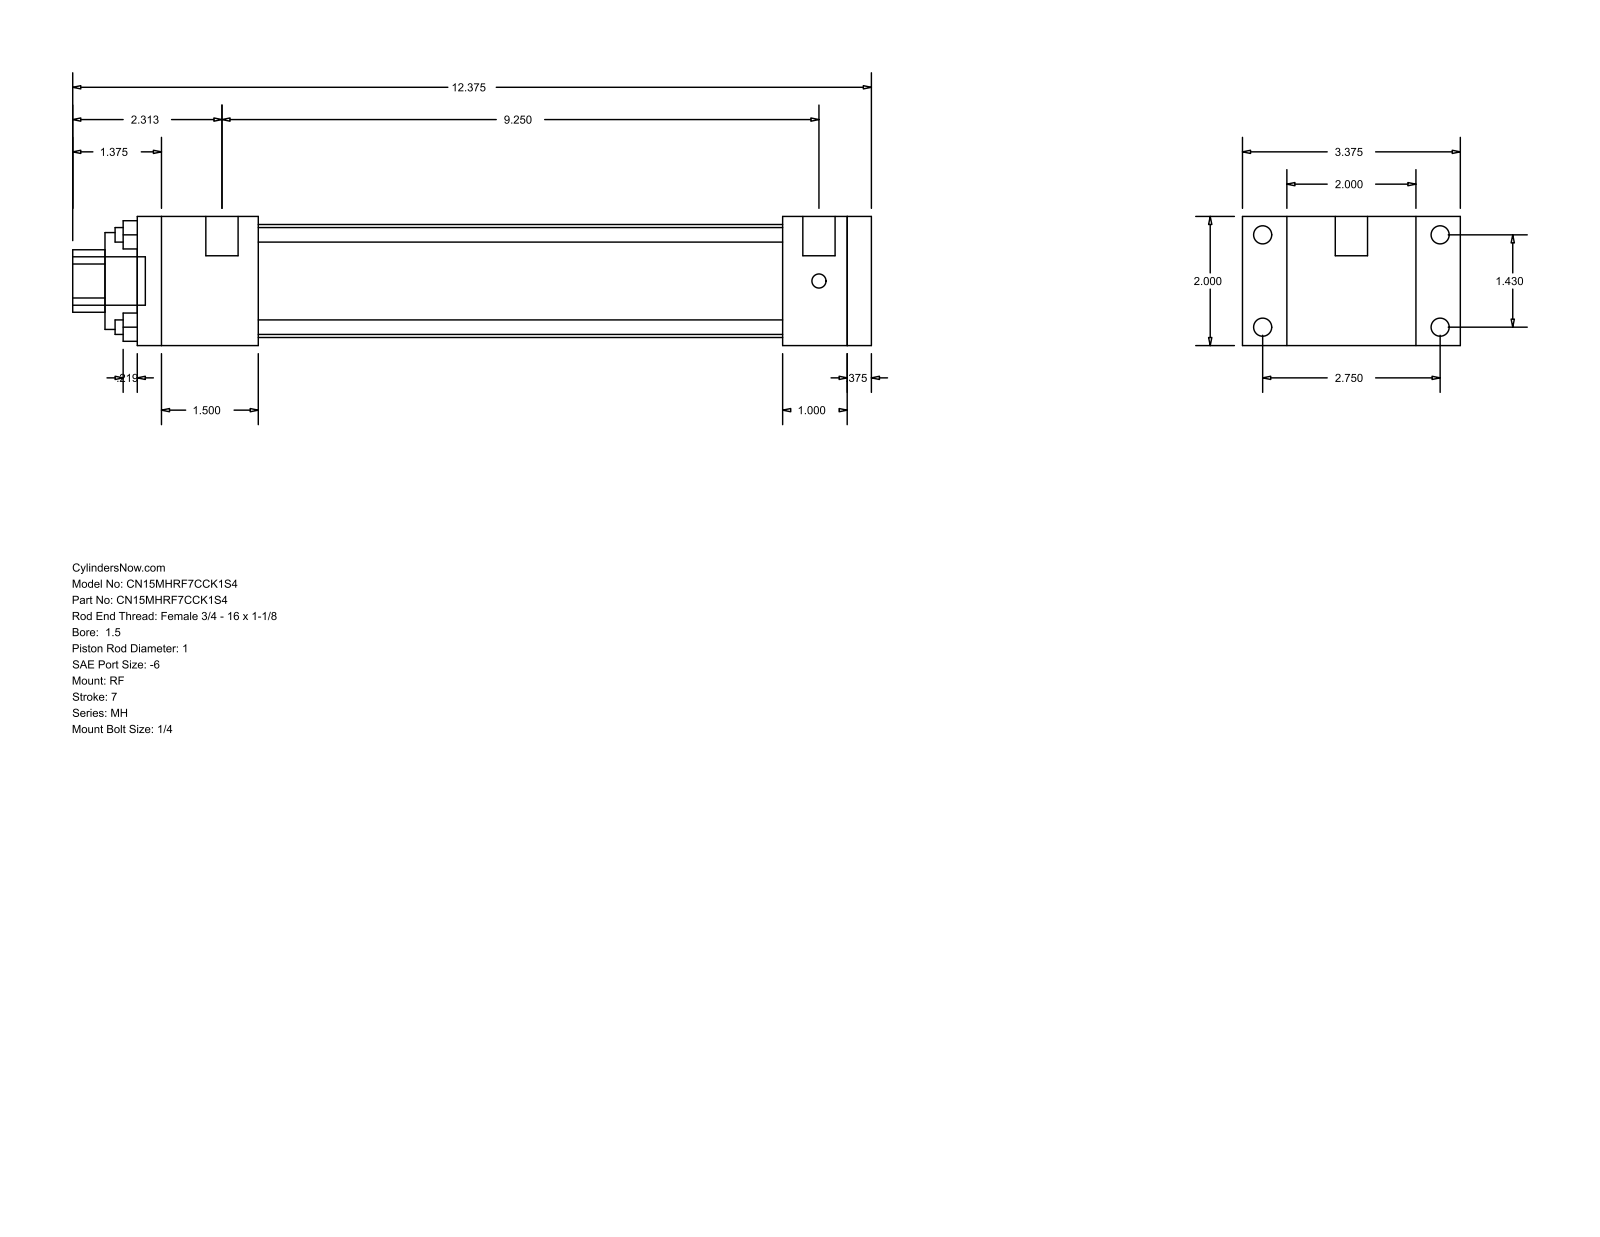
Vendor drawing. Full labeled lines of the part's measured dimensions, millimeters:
Part name (STEP PRODUCT): MH_RF__0150_1
STEP written by: GSSL Pune (CONFIG_CONTROL_DESIGN)
Units: millimetres
Bodies: 0 solids, 92 faces (64 planar, 28 cylindrical, 0 other)
Overall size (bounding box): 314.32 × 85.72 × 50.8
Round holes (diameter × count): ⌀5.71 ×4, ⌀25.4 ×1, ⌀38.1 ×1, ⌀44.45 ×1
Round bosses / shafts (diameter × count): ⌀7.14 ×4, ⌀5.56 ×4, ⌀12.7 ×2, ⌀19.05 ×1
Partial cylindrical surfaces — rounded edges, fillets, slot ends (radius × count): R12.29 ×1
Main face-to-face distances: 50.8, 9.52, 279.4, 25.4, 288.92, 17.46, 68.26, 254, 34.92, 47.63
Hole centre spacings: 25.68, 36.32, 51.36
